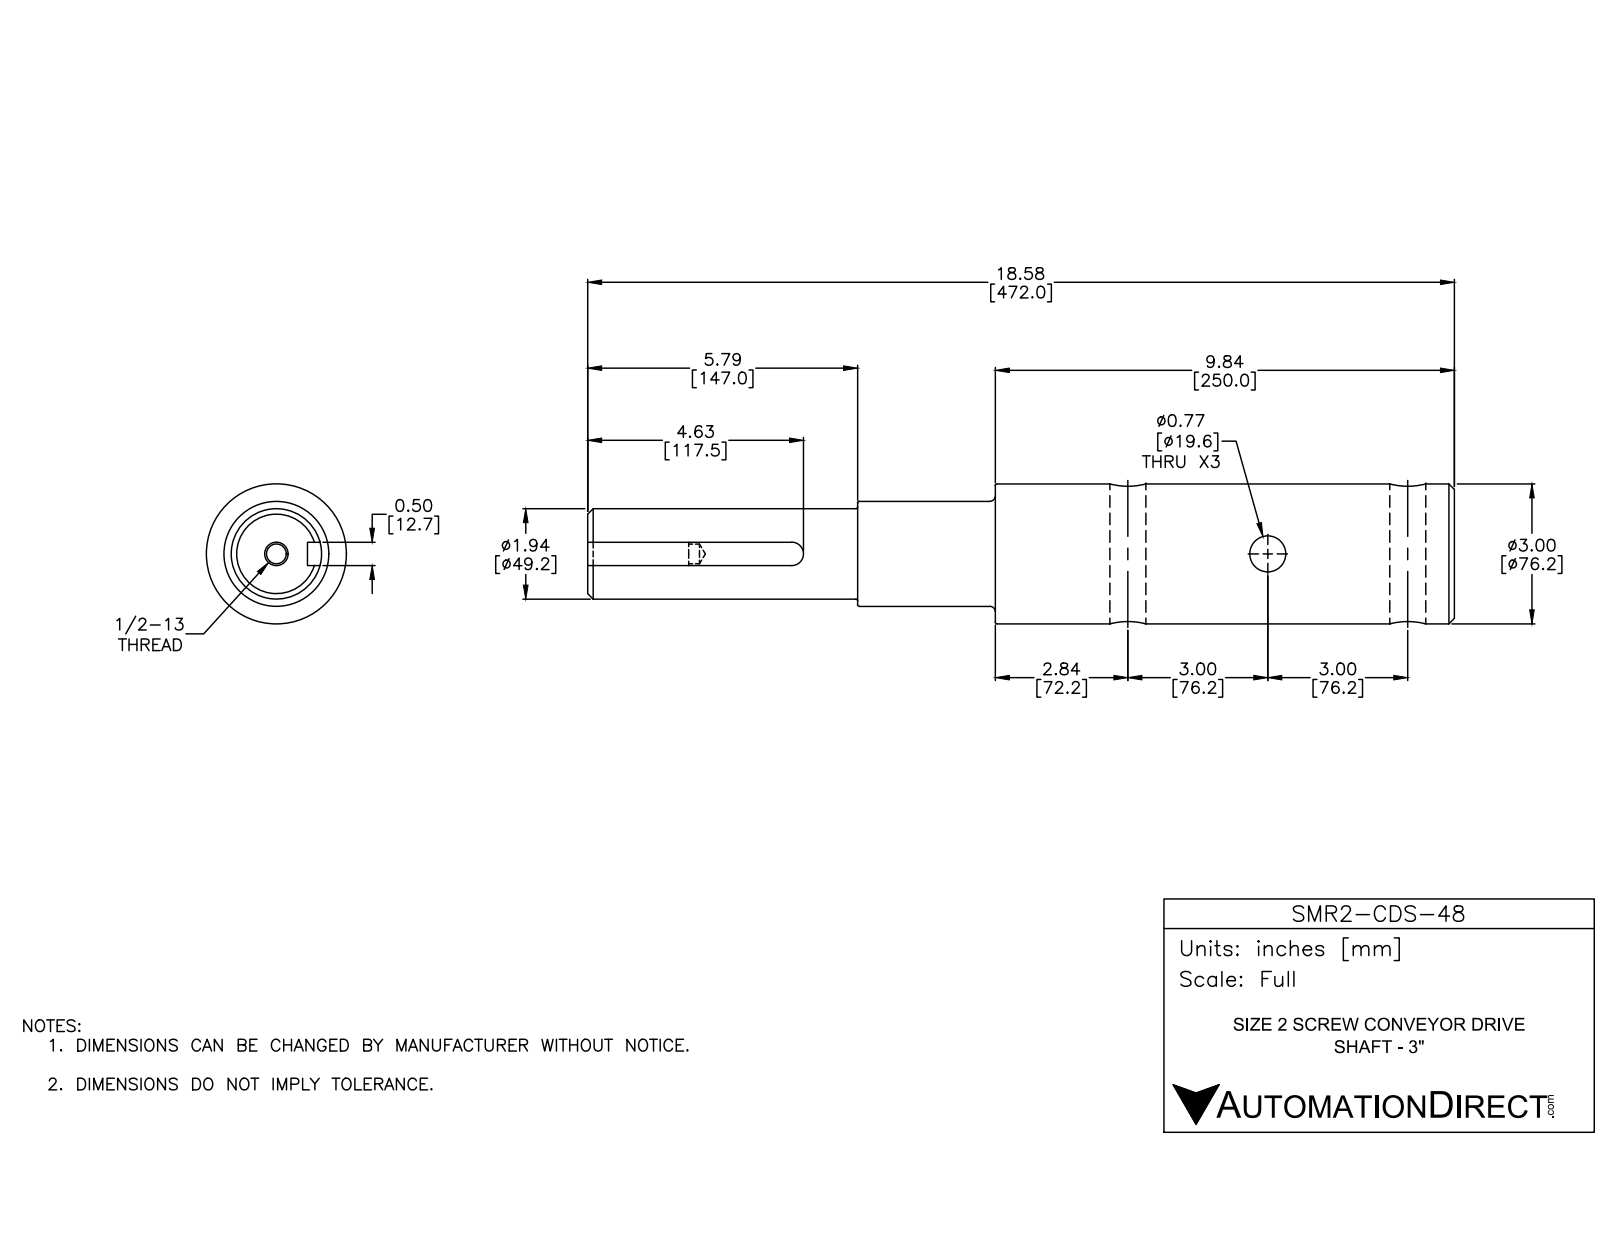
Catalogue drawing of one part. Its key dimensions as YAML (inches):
part_name: "SMR2-CDS-48"
step_written_by: "SolidWorks 2016 (AUTOMOTIVE_DESIGN)"
units: inches
bodies: {solids: 1, faces: 40, planar: 8, cylindrical: 18, other: 14}
overall_size: [18.581, 3, 3]
volume: 92.97
surface_area: 185.9
round_holes:
  - {diameter: 0.772, count: 3}
  - {diameter: 0.422, count: 1}
  - {diameter: 0.5, count: 1}
round_bosses_or_shafts:
  - {diameter: 3, count: 1}
  - {diameter: 2.25, count: 1}
  - {diameter: 1.937, count: 1}
partial_cylinders:
  - {radius: 0.25, count: 1}
face_to_face_distances: [18.581, 8.74, 9.841, 0.5, 5.787, 2.953, 12.793, 2.165, 3.622, 6.575]
hole_center_spacings: [6]
